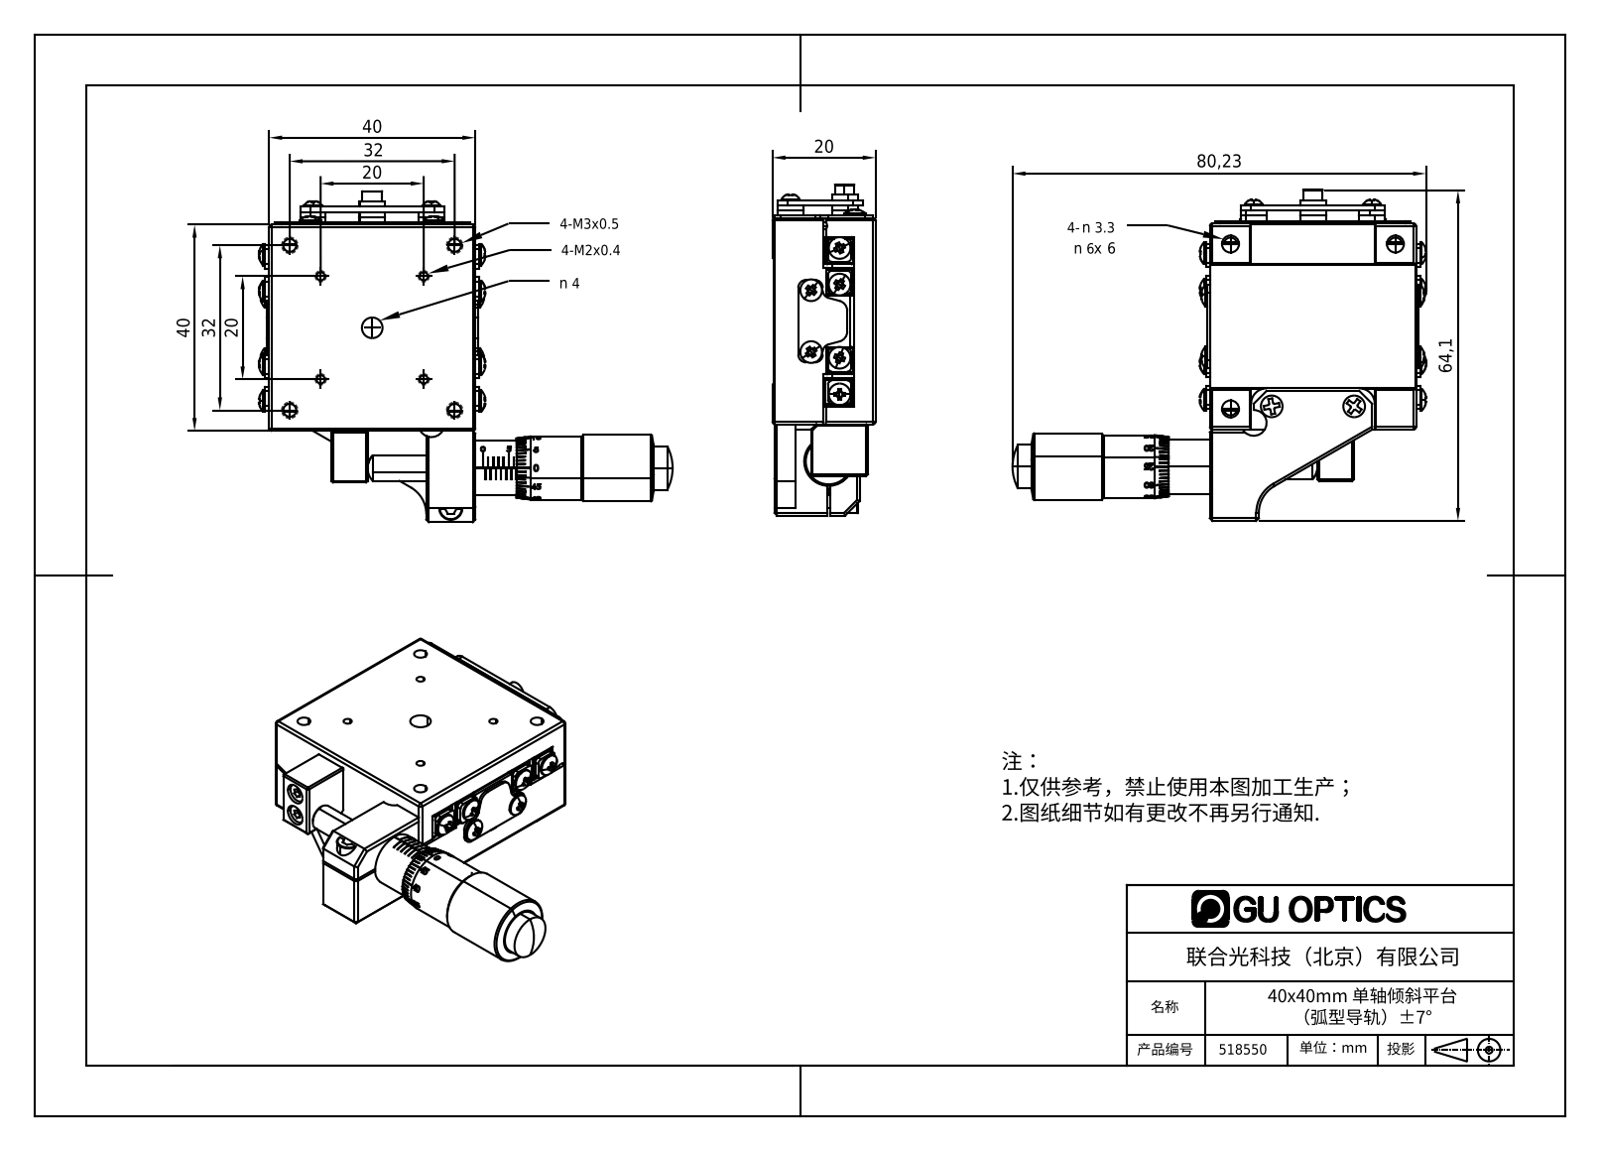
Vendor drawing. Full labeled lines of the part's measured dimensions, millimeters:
Part name (STEP PRODUCT): MXG4-40VM
STEP written by: SolidWorks 2020 (CONFIG_CONTROL_DESIGN)
Units: millimetres
Bodies: 2 solids, 1508 faces (998 planar, 318 cylindrical, 192 other)
Overall size (bounding box): 80.23 × 64.2 × 20
Volume: 36 683 mm³ · Surface area: 19 308 mm²
Round holes (diameter × count): ⌀1.6 ×4, ⌀2.5 ×4, ⌀6 ×4, ⌀3.3 ×3, ⌀4 ×3, ⌀8.2 ×1, ⌀9.5 ×1, ⌀10.7 ×1
Round bosses / shafts (diameter × count): ⌀4.2 ×8, ⌀5 ×4, ⌀3.8 ×3, ⌀3.5 ×2, ⌀13 ×1, ⌀12.25 ×1, ⌀10.5 ×1, ⌀10 ×1
Partial cylindrical surfaces — rounded edges, fillets, slot ends (radius × count): R0.8 ×16, R0.5 ×12, R1.5 ×12, R2 ×10, R1 ×8, R3 ×4, R2.25 ×1, R2.5 ×1
Main face-to-face distances: 19.7, 40.5, 40, 19.6, 0.8, 21.3, 1, 0.5, 3, 0.4
Hole centre spacings: 26.68, 8.49, 14.14, 20, 22.63, 32, 36.77, 28.28
